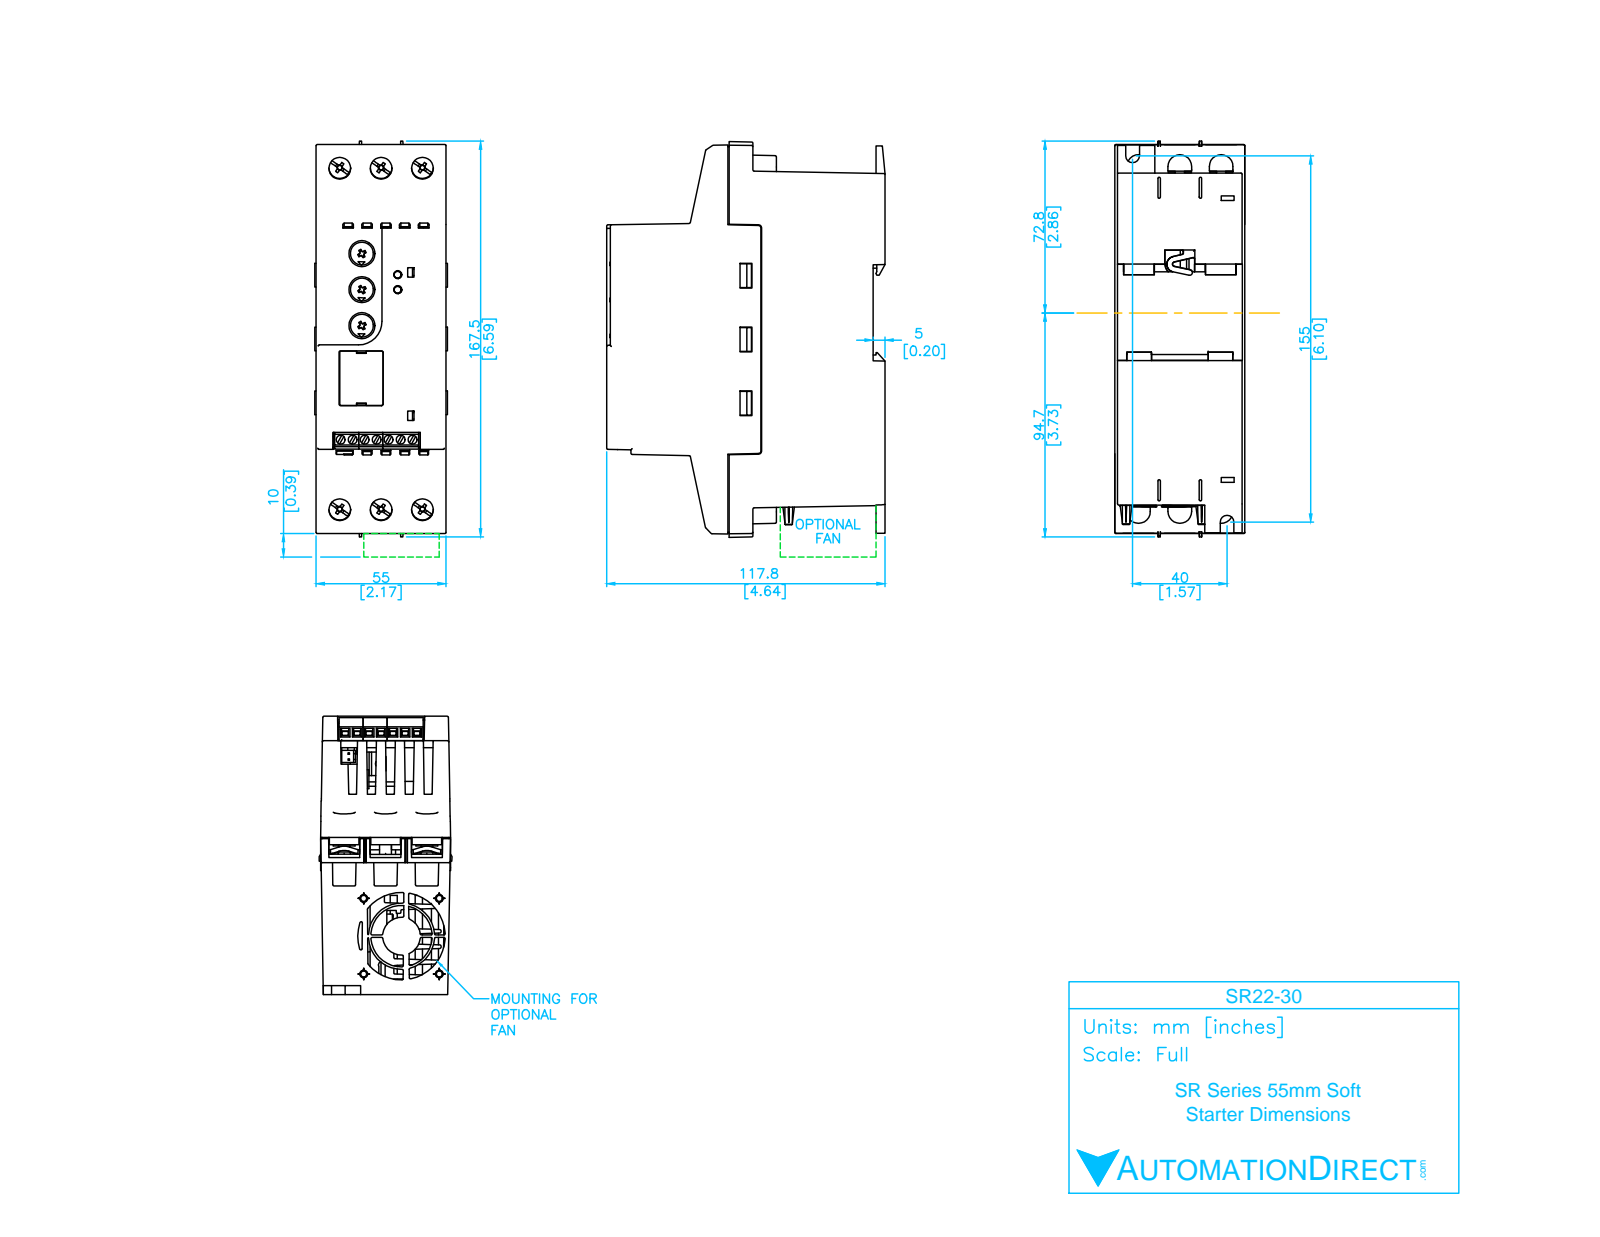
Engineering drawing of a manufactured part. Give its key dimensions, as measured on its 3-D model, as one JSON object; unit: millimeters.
{"part_name": "SR22-30", "step_written_by": "SolidWorks 2013 (AUTOMOTIVE_DESIGN)", "units": "millimeters", "bodies": {"solids": 1, "faces": 623, "planar": 483, "cylindrical": 110, "other": 30}, "overall_size": [164.5, 117.8, 55.87], "volume_mm3": 813460, "surface_area_mm2": 69575, "round_holes": [[3.5, 7], [9.5, 6], [11.3, 3], [4, 2], [27.66, 1], [40.29, 1]], "round_bosses_or_shafts": [[10.44, 3], [29.09, 1], [16, 1]], "partial_cylinders_radius": [[0.5, 35], [4.88, 6], [1, 2], [2.75, 2], [10, 1]], "face_to_face_distances": [54.97, 54.94, 55, 117.8, 5.14, 112.66, 141.5, 18, 0.5, 1.5], "hole_center_spacings": [5.25, 10.5, 15.75, 18, 137.19, 21, 136, 15]}
